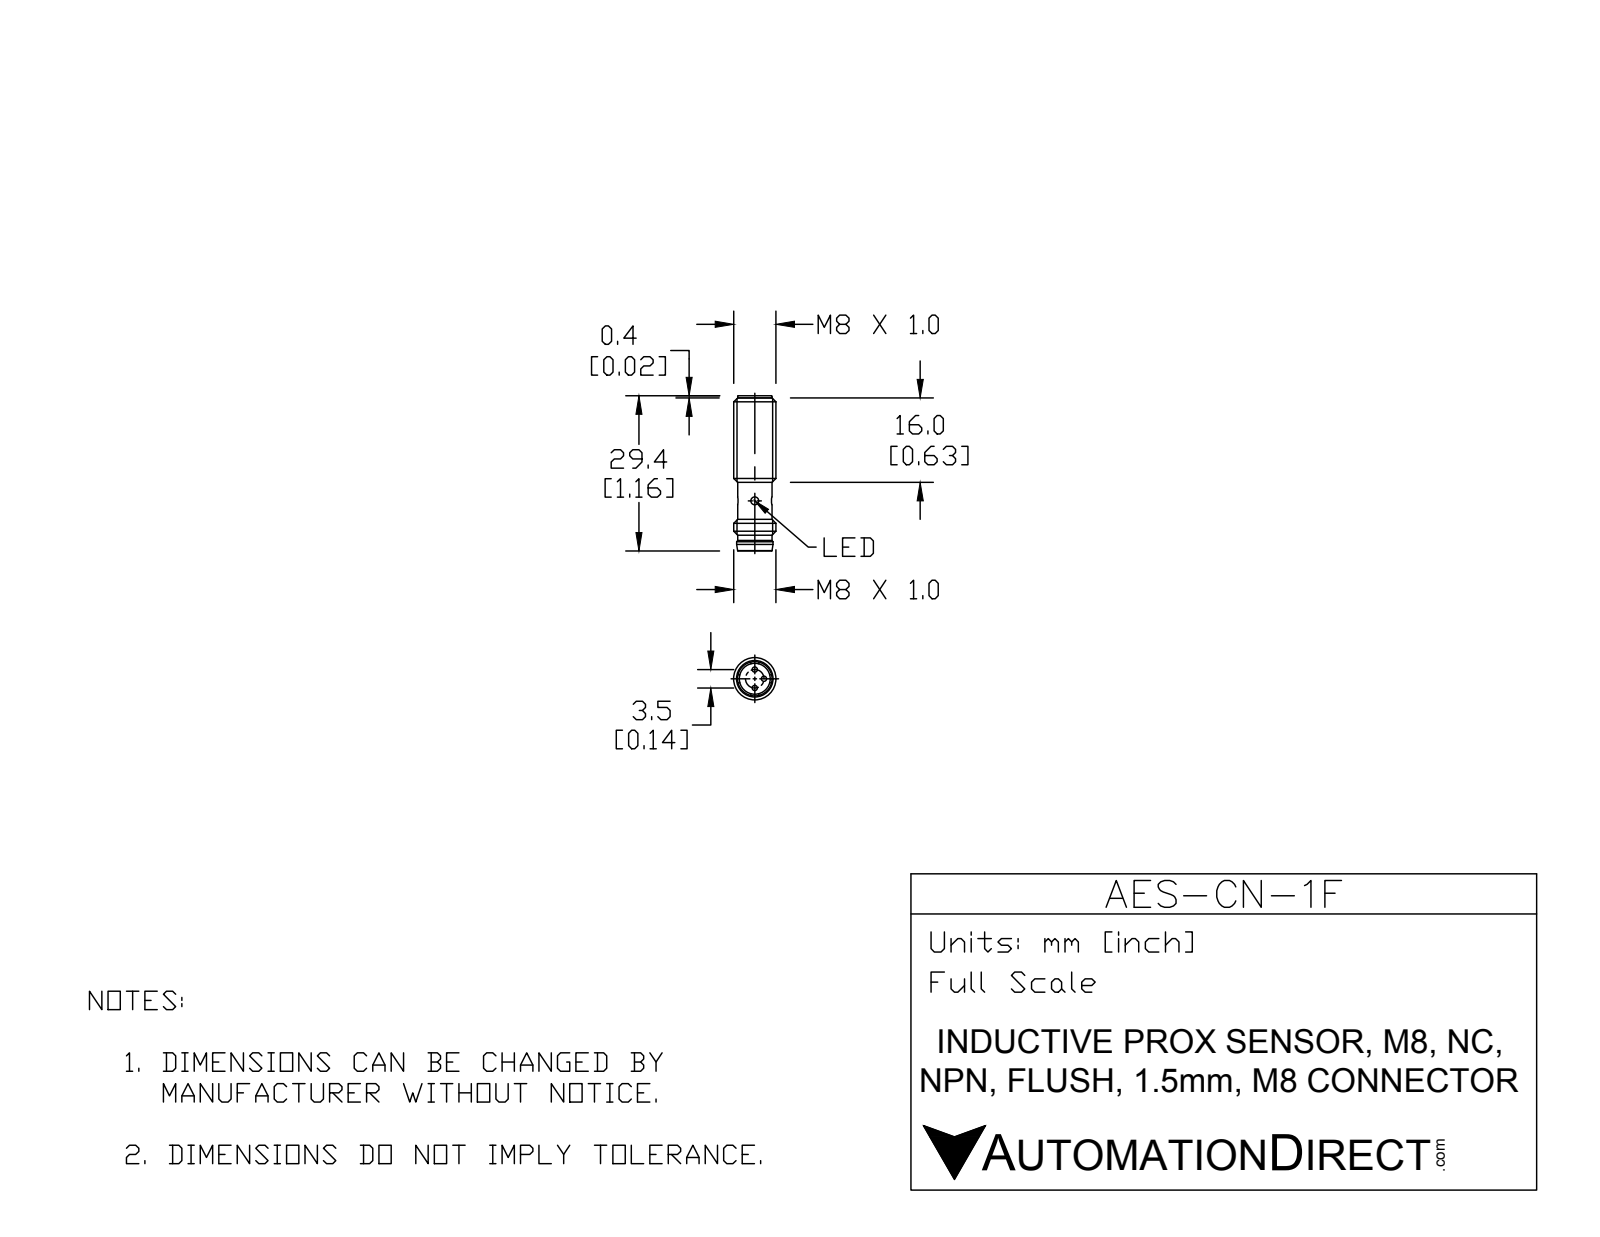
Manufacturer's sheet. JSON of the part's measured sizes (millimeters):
{"part_name": "AES-CN-1F", "step_written_by": "SolidWorks 2015 (CONFIG_CONTROL_DESIGN)", "units": "millimeters", "bodies": {"solids": 1, "faces": 58, "planar": 10, "cylindrical": 28, "other": 20}, "overall_size": [29.4, 8, 8], "volume_mm3": 1157, "surface_area_mm2": 928, "round_holes": [[1.5, 2], [5.85, 1]], "round_bosses_or_shafts": [[1, 3], [8, 1], [6.9, 1], [6.5, 1]], "face_to_face_distances": [24.4, 3, 27.4, 5.5, 11, 8, 16.4, 27, 24, 16]}
